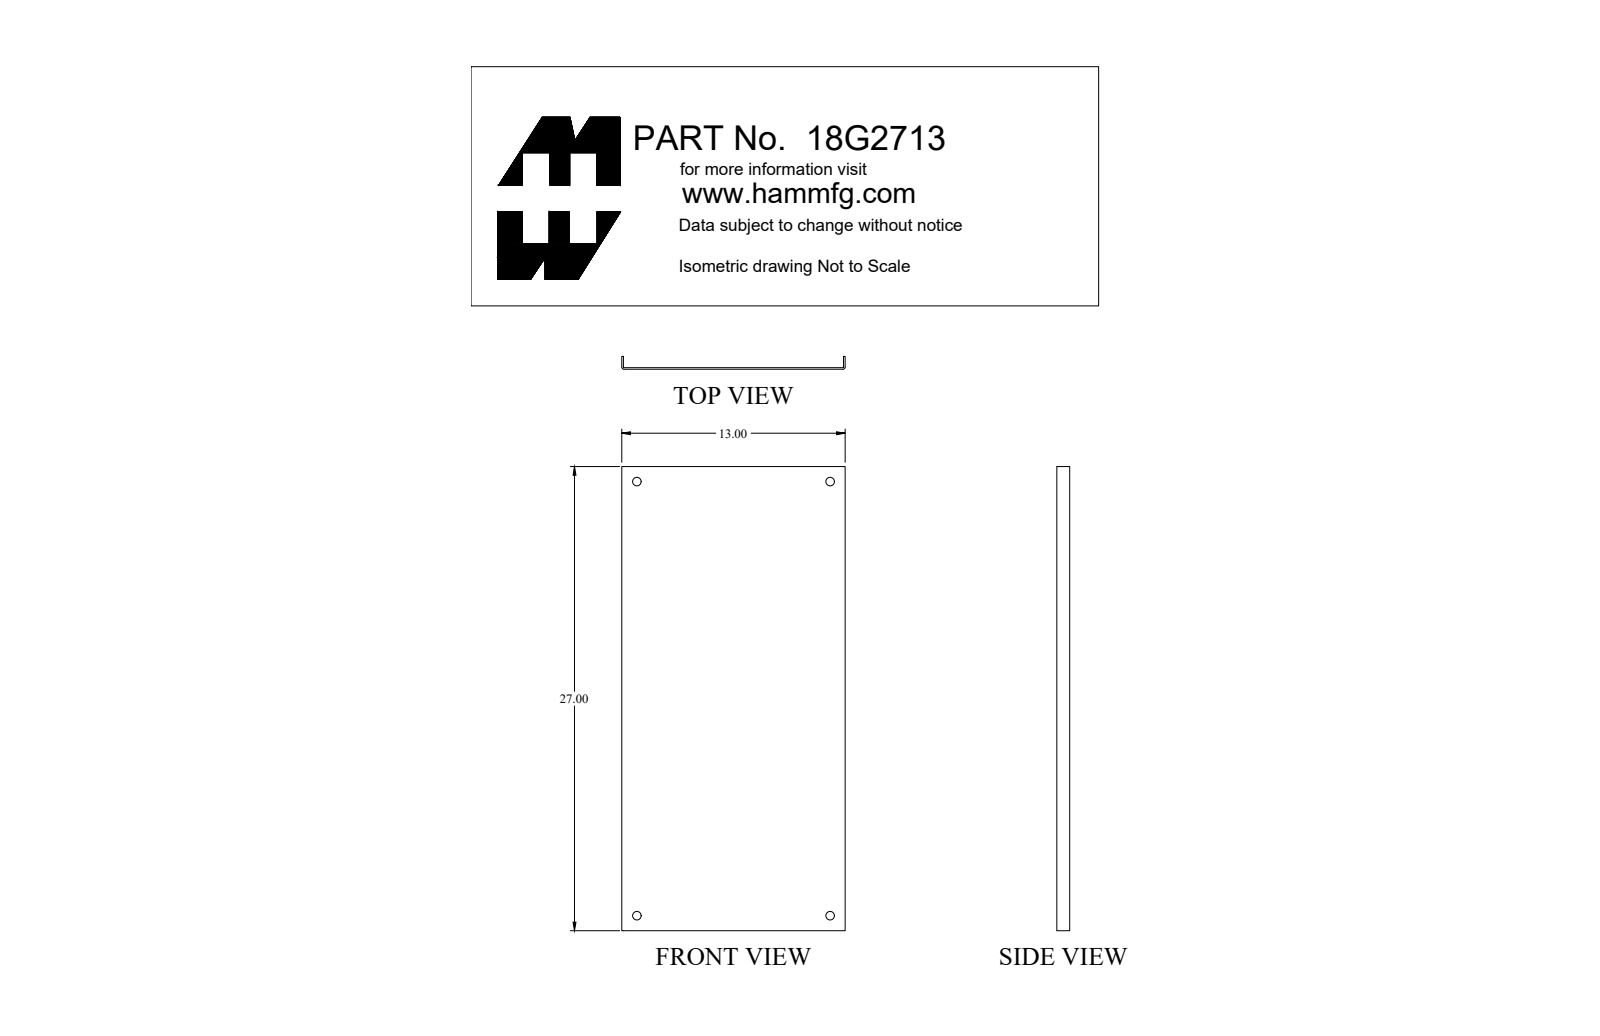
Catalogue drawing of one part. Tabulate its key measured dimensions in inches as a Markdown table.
| quantity | value |
| --- | --- |
| part name | 18G2713 |
| STEP written by | SolidWorks 2018 (AUTOMOTIVE_DESIGN) |
| units | inches |
| bodies | 1 solid, 18 faces (10 planar, 8 cylindrical, 0 other) |
| overall size | 27 × 13 × 0.75 |
| volume | 36.46 in³ |
| surface area | 776 in² |
| round holes (diameter × count) | 0.5 × 4 |
| partial cylindrical surfaces (radius × count) | 0.03 × 2, 0.125 × 2 |
| main face-to-face distances | 0.095, 12.905, 13, 12.81, 0.75, 0.655, 27 |
| hole center spacings | 11.25, 25.25, 27.643 |
